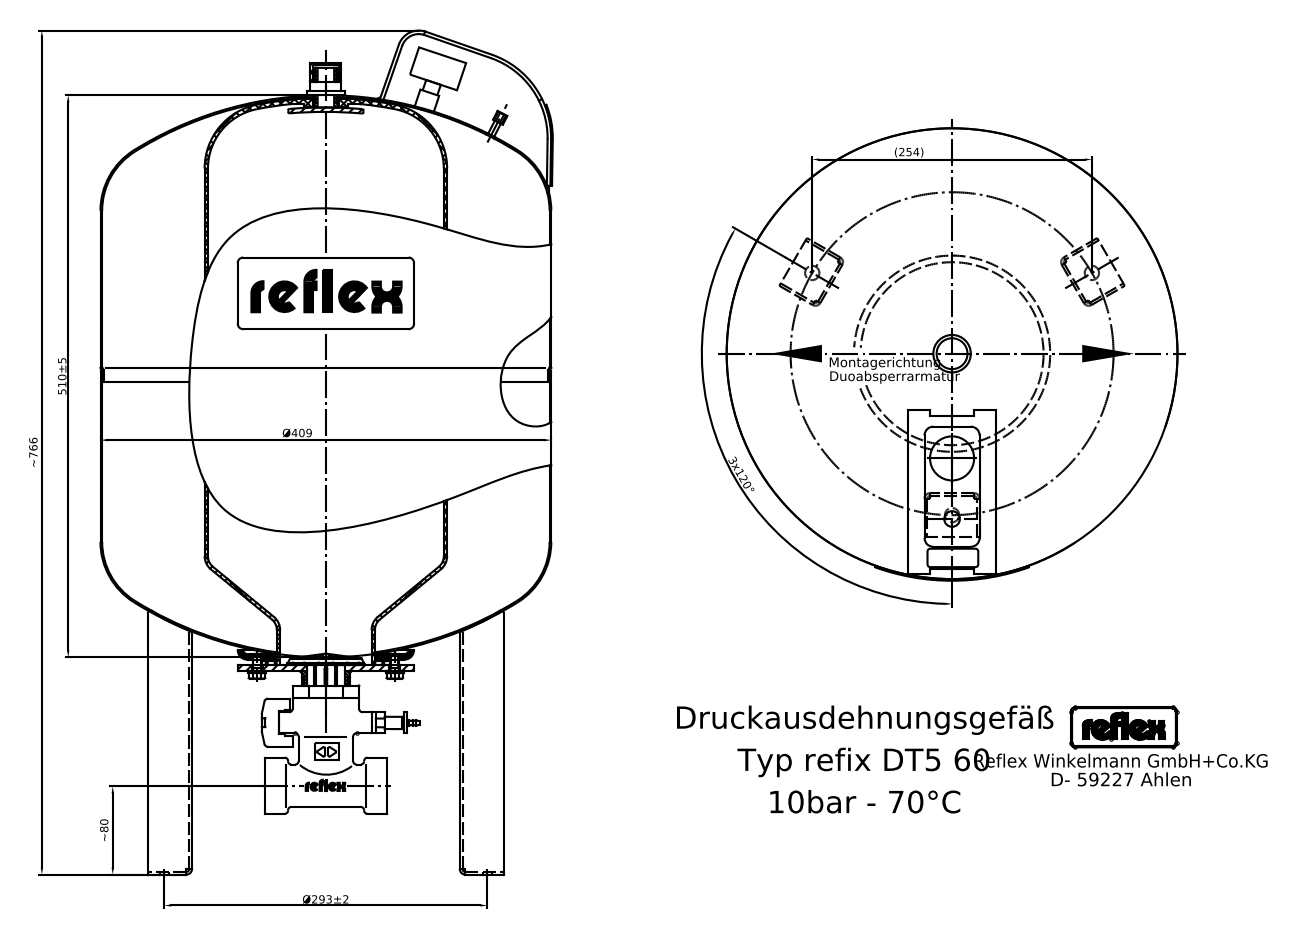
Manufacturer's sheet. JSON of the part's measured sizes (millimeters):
{"step_written_by": "Mechanical Desktop 2008 (CONFIG_CONTROL_DESIGN)", "units": "millimeters", "bodies": {"solids": 21, "faces": 670, "planar": 286, "cylindrical": 247, "other": 137}, "overall_size": [761.11, 409, 409], "volume_mm3": 57510000, "surface_area_mm2": 1674000, "round_holes": [[13.4, 3], [2.48, 1], [3.8, 1], [4.3, 1], [4.4, 1], [5.45, 1], [7, 1], [8, 1], [11.4, 1], [42.4, 1], [92, 1], [150, 1]], "round_bosses_or_shafts": [[10, 9], [409, 1], [160, 1], [140, 1], [62, 1], [56, 1], [53, 1], [52, 1]], "partial_cylinders_radius": [[0.5, 20], [1, 15], [2.5, 15], [5, 15], [3.94, 4], [1.57, 3], [2.69, 2], [4.72, 2]], "face_to_face_distances": [280, 2.5, 47.5, 45, 50, 121, 401, 6, 127, 407], "hole_center_spacings": [146.5, 253.74]}
